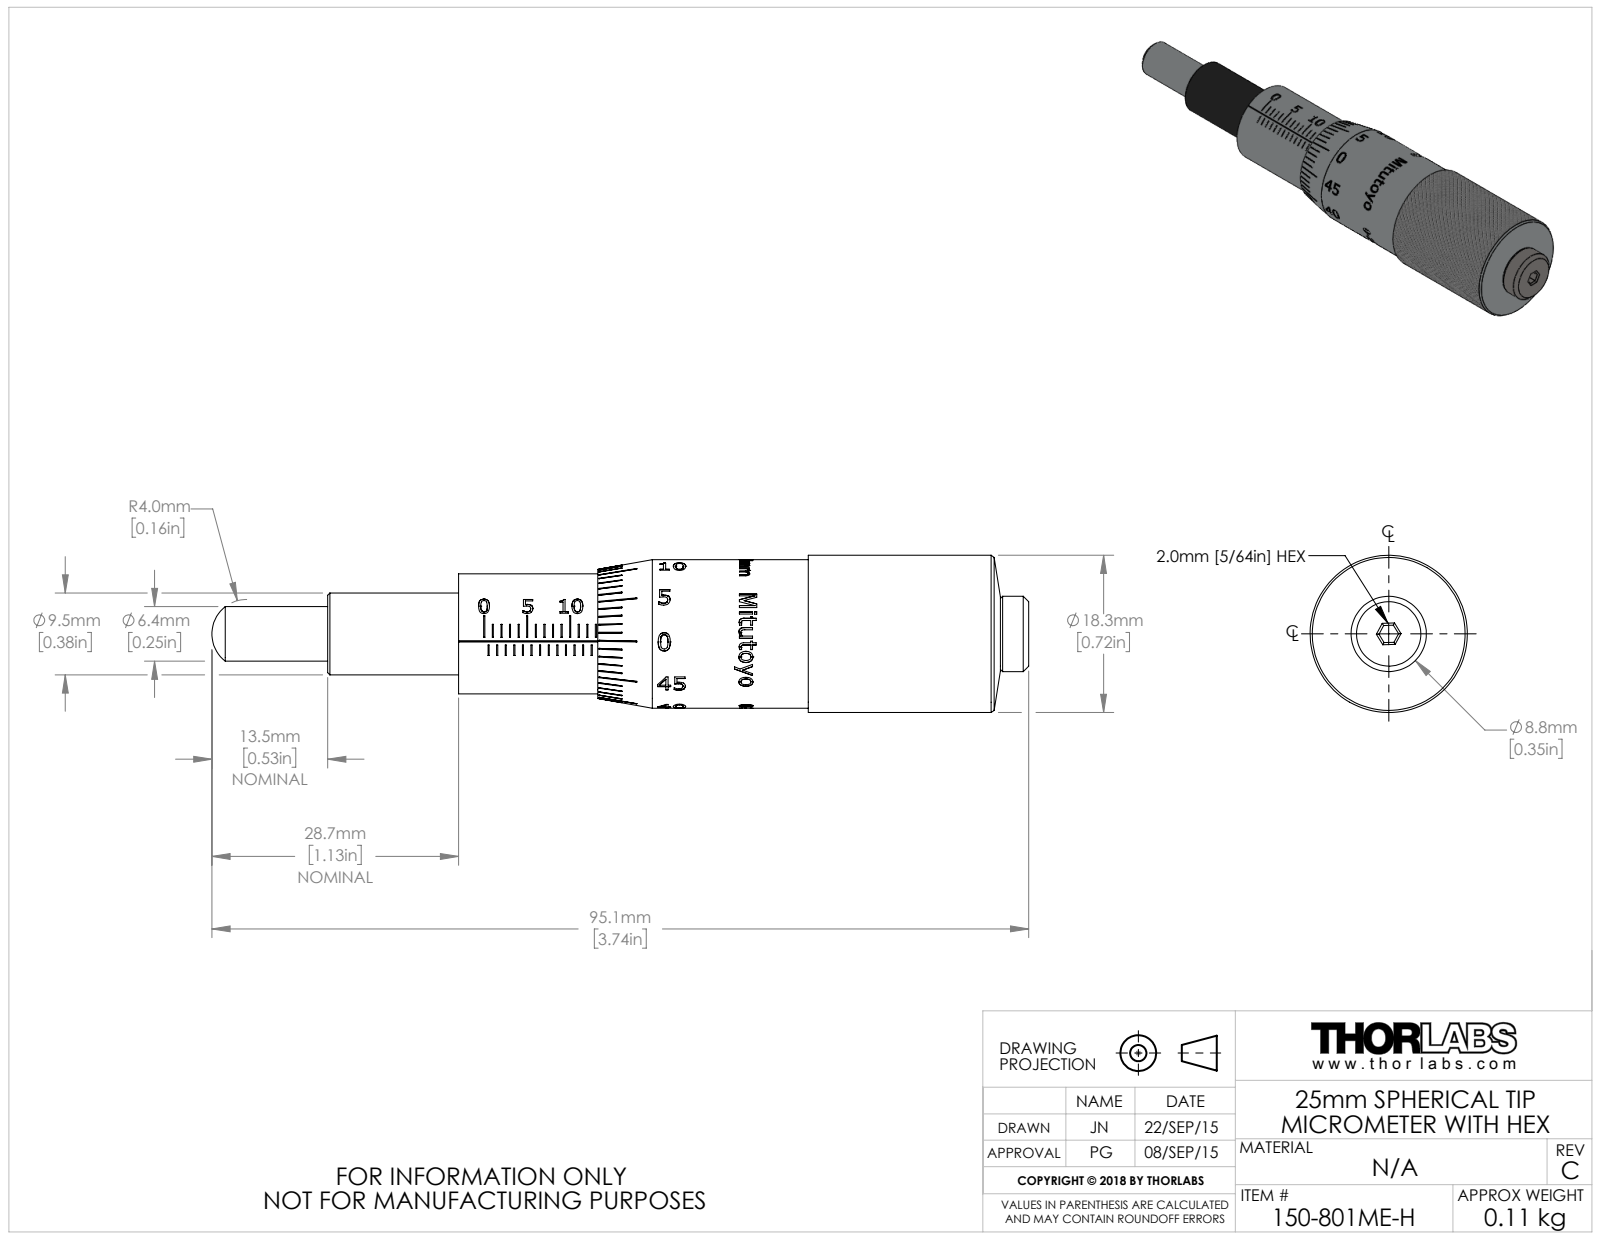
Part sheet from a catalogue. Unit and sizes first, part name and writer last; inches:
Units: inches
Overall size (bounding box): 3.744 × 0.72 × 0.72
Round holes (diameter × count): ⌀0.157 ×1, ⌀0.25 ×1, ⌀0.56 ×1
Round bosses / shafts (diameter × count): ⌀0.72 ×1, ⌀0.68 ×1, ⌀0.55 ×1, ⌀0.44 ×1, ⌀0.375 ×1, ⌀0.345 ×1, ⌀0.137 ×1
Partial cylindrical surfaces — rounded edges, fillets, slot ends (radius × count): R0.274 ×1, R0.297 ×1, R0.315 ×1, R0.327 ×1, R0.339 ×1
Main face-to-face distances: 0.33, 0.933, 2.153, 2.483, 1.55, 0.603, 1.22, 1.263, 2.613, 1.393
Volume: 0.791 in³ · Surface area: 15.85 in²
Bodies: 3 solids, 1359 faces (630 planar, 242 cylindrical, 487 other)
Part name (STEP PRODUCT): TTN045983-E0W
STEP written by: SolidWorks 2016 (AUTOMOTIVE_DESIGN)
